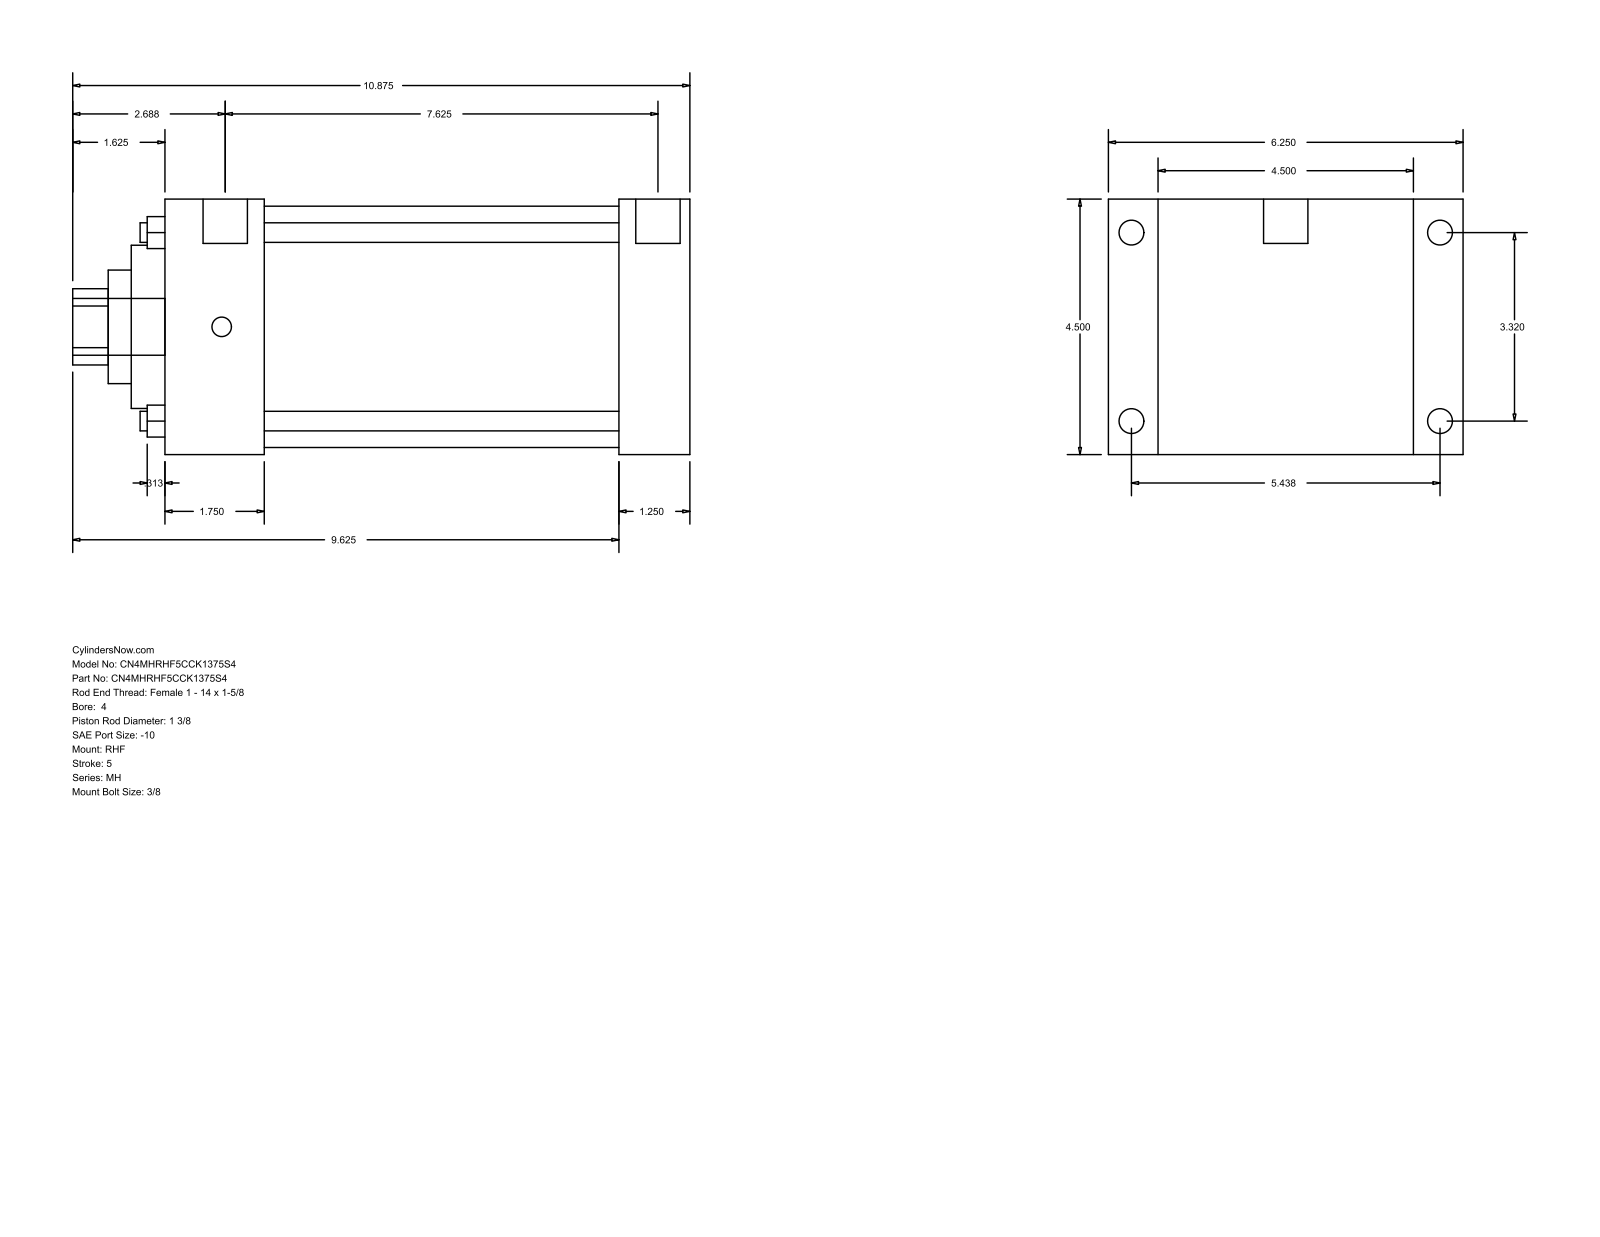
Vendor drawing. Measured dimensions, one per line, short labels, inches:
name: MH_RHF__0400_1.375
written by: GSSL Pune (CONFIG_CONTROL_DESIGN)
unit: in
bodies: 0 solids, 90 faces (61 planar, 29 cylindrical, 0 other)
size: 10.875 × 6.25 × 4.5
holes: 4× ⌀0.345, 1× ⌀1.375, 1× ⌀2, 1× ⌀2.875, 1× ⌀4.25
bosses: 4× ⌀0.438, 4× ⌀0.344, 2× ⌀0.781, 1× ⌀1
rounds: 1× R0.672
face distances: 4.5, 9.25, 8, 1.25, 0.875, 5.375, 6.25, 1.75, 7.5, 6.25
hole spacings: 2.347, 3.32, 4.695
